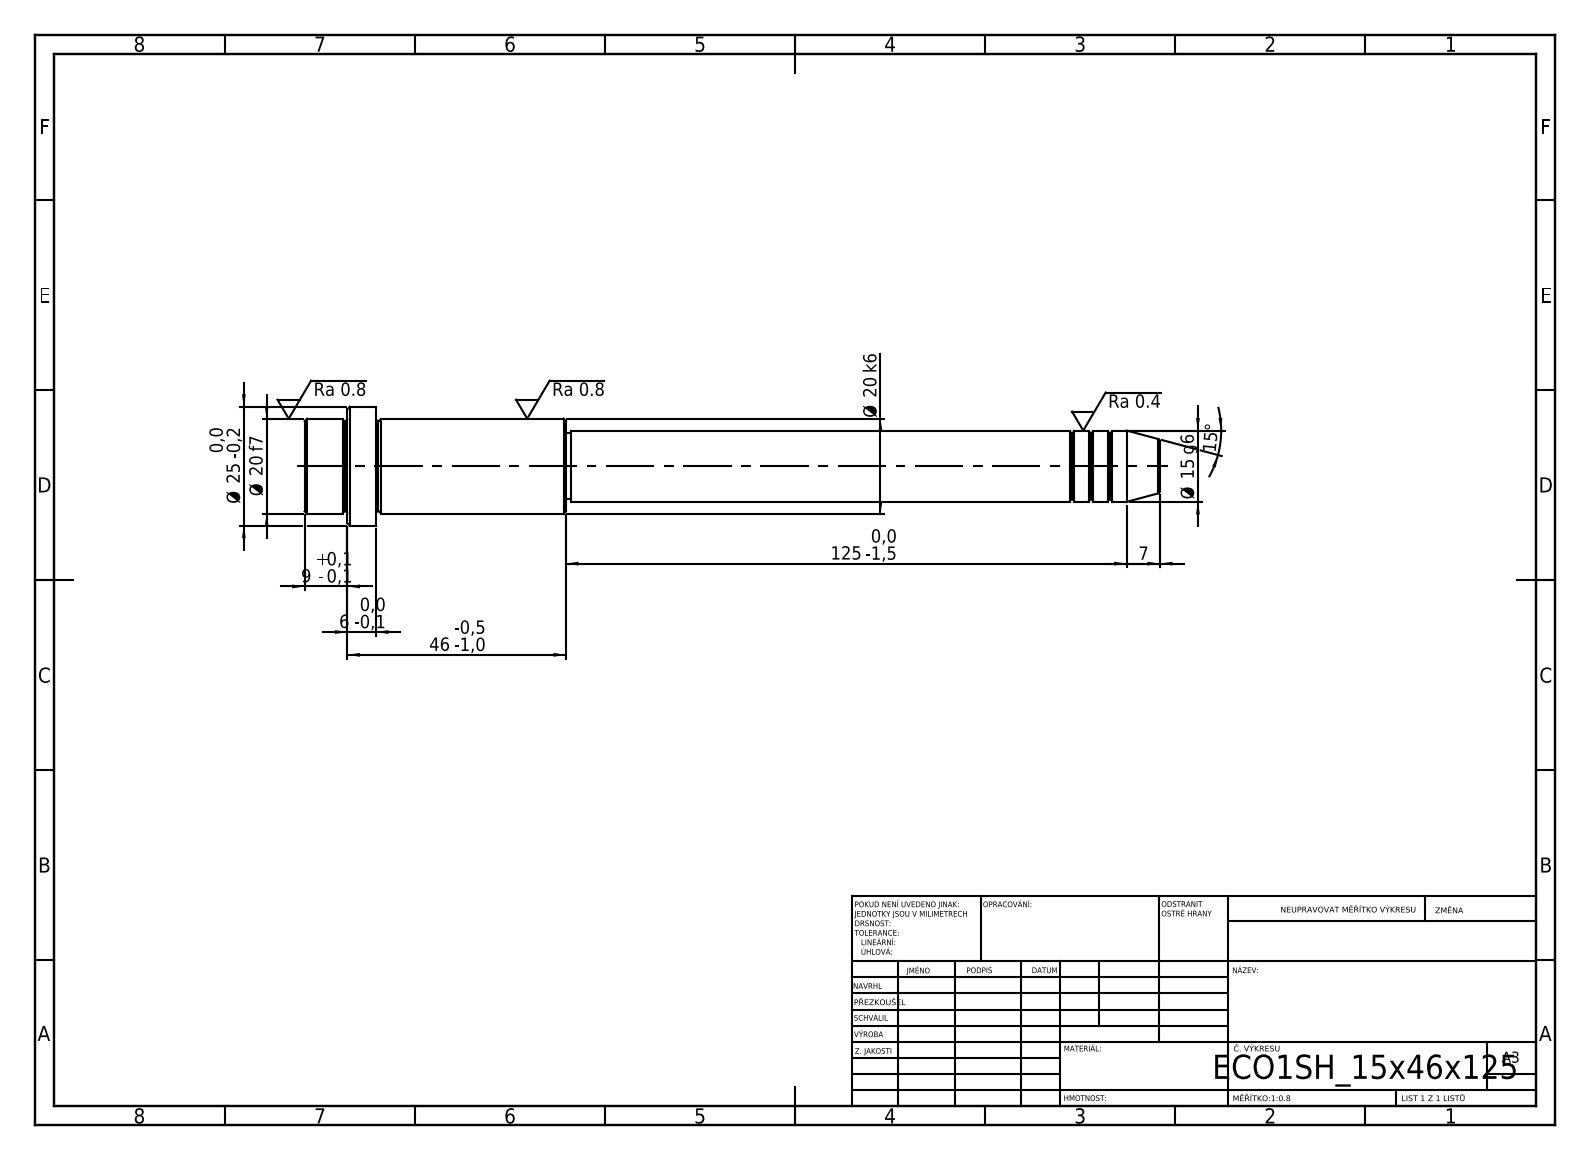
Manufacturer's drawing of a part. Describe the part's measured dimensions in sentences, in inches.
Its 3-D file was written by "SolidWorks 2019 (CONFIG_CONTROL_DESIGN)". It is 1 solid with 52 faces: 6 planar, 16 cylindrical and 30 other. Overall it measures 7.087 by 0.984 by 0.984 inches. Its volume is 2.441 cubic inches and its surface area 16.16 square inches. Round bosses or shafts: 1 of diameter 0.984, 1 of diameter 0.787, 1 of diameter 0.591, 1 of diameter 0.551. The main face-to-face distances are 0.591, 0.236, 0.354, 1.575, 1.811, 2.165, 4.921, 6.496, 6.732, 7.087.
